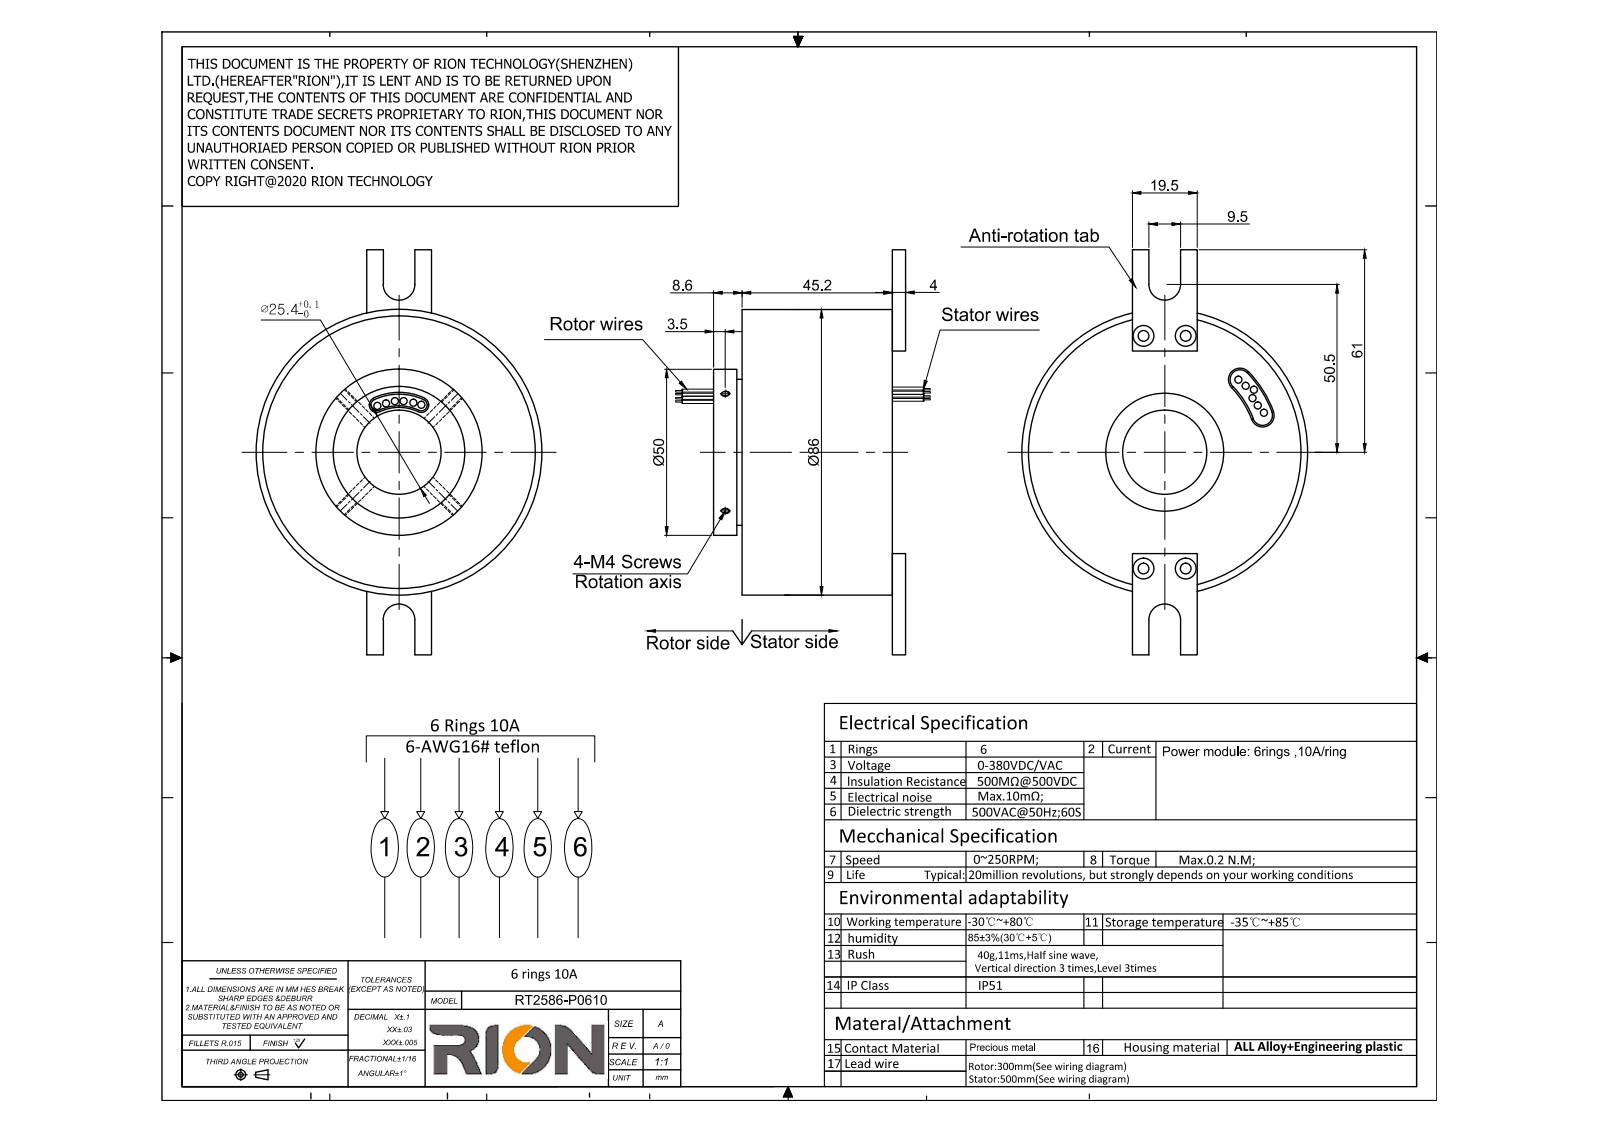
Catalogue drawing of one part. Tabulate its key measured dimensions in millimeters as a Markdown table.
| quantity | value |
| --- | --- |
| part name | RT2586-P0610 |
| STEP written by | SolidWorks 2014 (CONFIG_CONTROL_DESIGN) |
| units | millimeters |
| bodies | 1 solid, 151 faces (53 planar, 82 cylindrical, 16 other) |
| overall size | 122 × 86 × 71.8 |
| volume | 254 545 mm³ |
| surface area | 38 397 mm² |
| round holes (diameter × count) | 2.5 × 4, 3.2 × 4, 3.3 × 4, 25.4 × 1, 35.51 × 1, 39.61 × 1, 82 × 1 |
| round bosses / shafts (diameter × count) | 2.1 × 12, 86 × 1, 81.9 × 1, 81.8 × 1, 50 × 1, 44 × 1, 39.6 × 1, 35.5 × 1 |
| partial cylindrical surfaces (radius × count) | 2 × 4, 4.75 × 2, 14 × 1, 18 × 1 |
| main face-to-face distances | 45.2, 8.6, 53.8, 4, 57.8, 49.2, 7, 1.6, 46.8, 50.8 |
| hole center spacings | 35.57, 12.7, 70, 71.14 |
